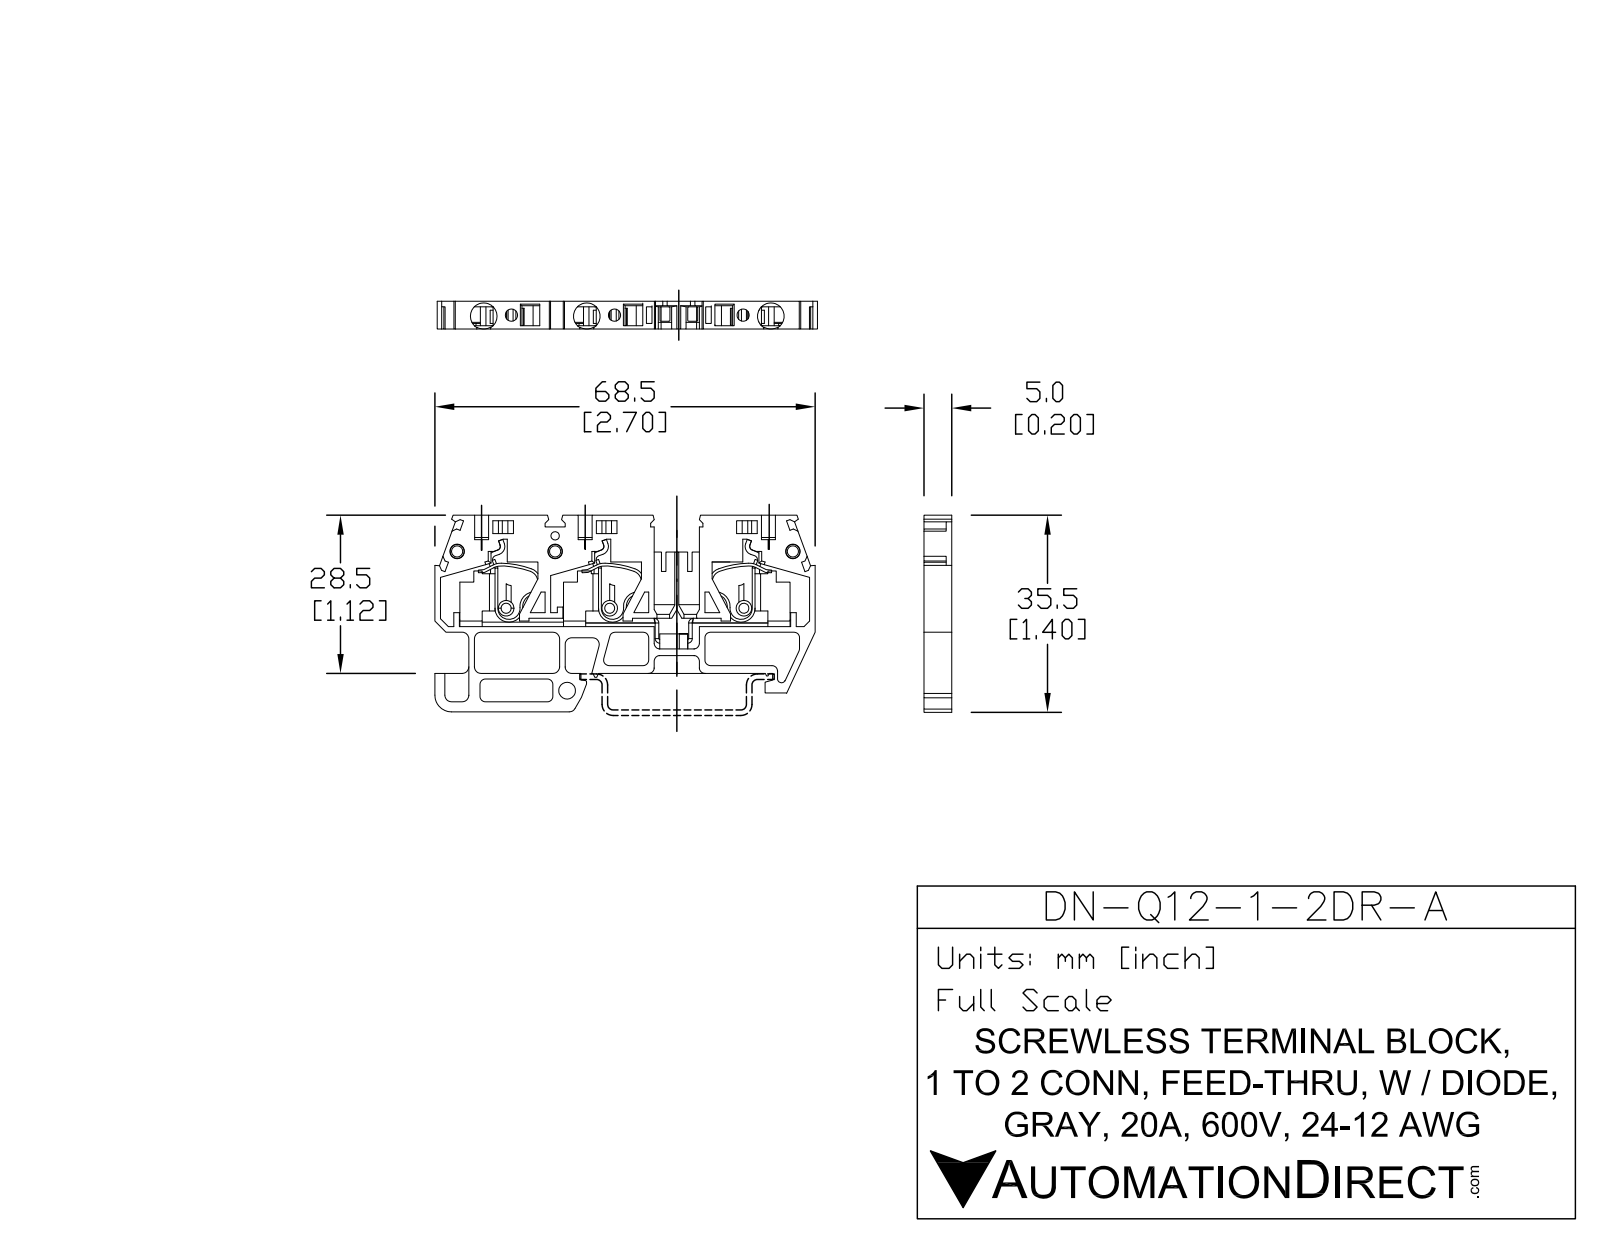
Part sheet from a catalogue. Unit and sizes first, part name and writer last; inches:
Units: inches
Overall size (bounding box): 2.701 × 1.394 × 0.197
Round holes (diameter × count): ⌀0.087 ×3, ⌀0.102 ×3, ⌀0.189 ×3, ⌀0.059 ×1, ⌀0.106 ×1, ⌀0.118 ×1
Round bosses / shafts (diameter × count): ⌀0.024 ×3
Partial cylindrical surfaces — rounded edges, fillets, slot ends (radius × count): R0.039 ×19, R0.047 ×12, R0.012 ×1, R0.028 ×1, R0.118 ×1
Main face-to-face distances: 0.197, 0.039, 0.079, 0.193, 0.118, 0.331, 0.047, 0.028, 0.295, 0.165
Hole centre spacings: 0.197, 0.732, 1.11, 1.843, 0.11, 0.535, 0.693, 0.702
Volume: 0.395 in³ · Surface area: 11.05 in²
Bodies: 1 solid, 400 faces (284 planar, 84 cylindrical, 32 other)
Part name (STEP PRODUCT): 42413D6_DN-Q12-1-2-DR-A; 20310_Piega3; 42413D6-DN-Q12-1-2-DR-A1
STEP written by: SolidWorks 2013 (AUTOMOTIVE_DESIGN)
